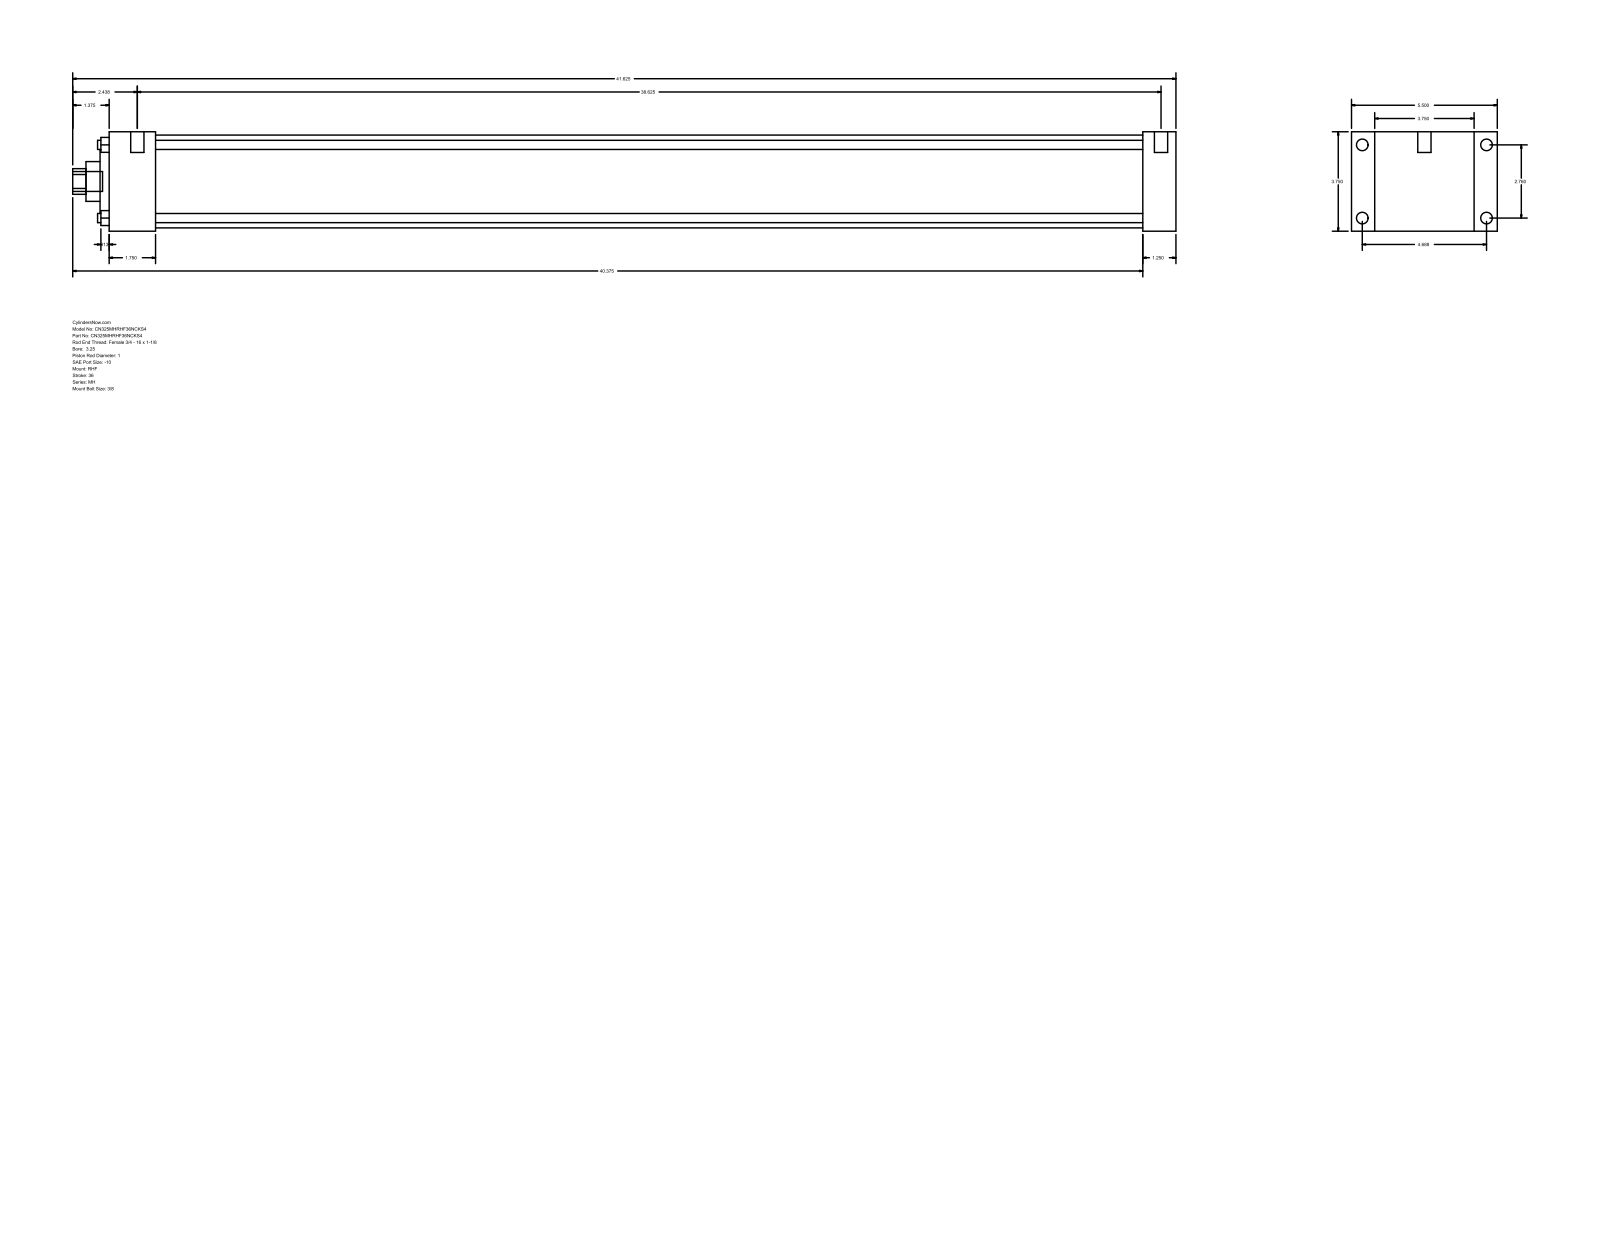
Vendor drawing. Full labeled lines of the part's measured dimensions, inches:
Part name (STEP PRODUCT): MH_RHF__0325_1
STEP written by: GSSL Pune (CONFIG_CONTROL_DESIGN)
Units: inches
Bodies: 0 solids, 90 faces (61 planar, 29 cylindrical, 0 other)
Overall size (bounding box): 41.625 × 5.5 × 3.75
Round holes (diameter × count): ⌀0.345 ×4, ⌀1 ×1, ⌀1.5 ×1, ⌀2.375 ×1, ⌀3.5 ×1
Round bosses / shafts (diameter × count): ⌀0.438 ×4, ⌀0.219 ×4, ⌀0.5 ×2, ⌀0.75 ×1
Partial cylindrical surfaces — rounded edges, fillets, slot ends (radius × count): R0.484 ×1
Main face-to-face distances: 3.75, 1.25, 0.875, 4.625, 39, 40.25, 5.5, 1.75, 37.25, 38.5
Hole centre spacings: 1.952, 2.76, 3.903
